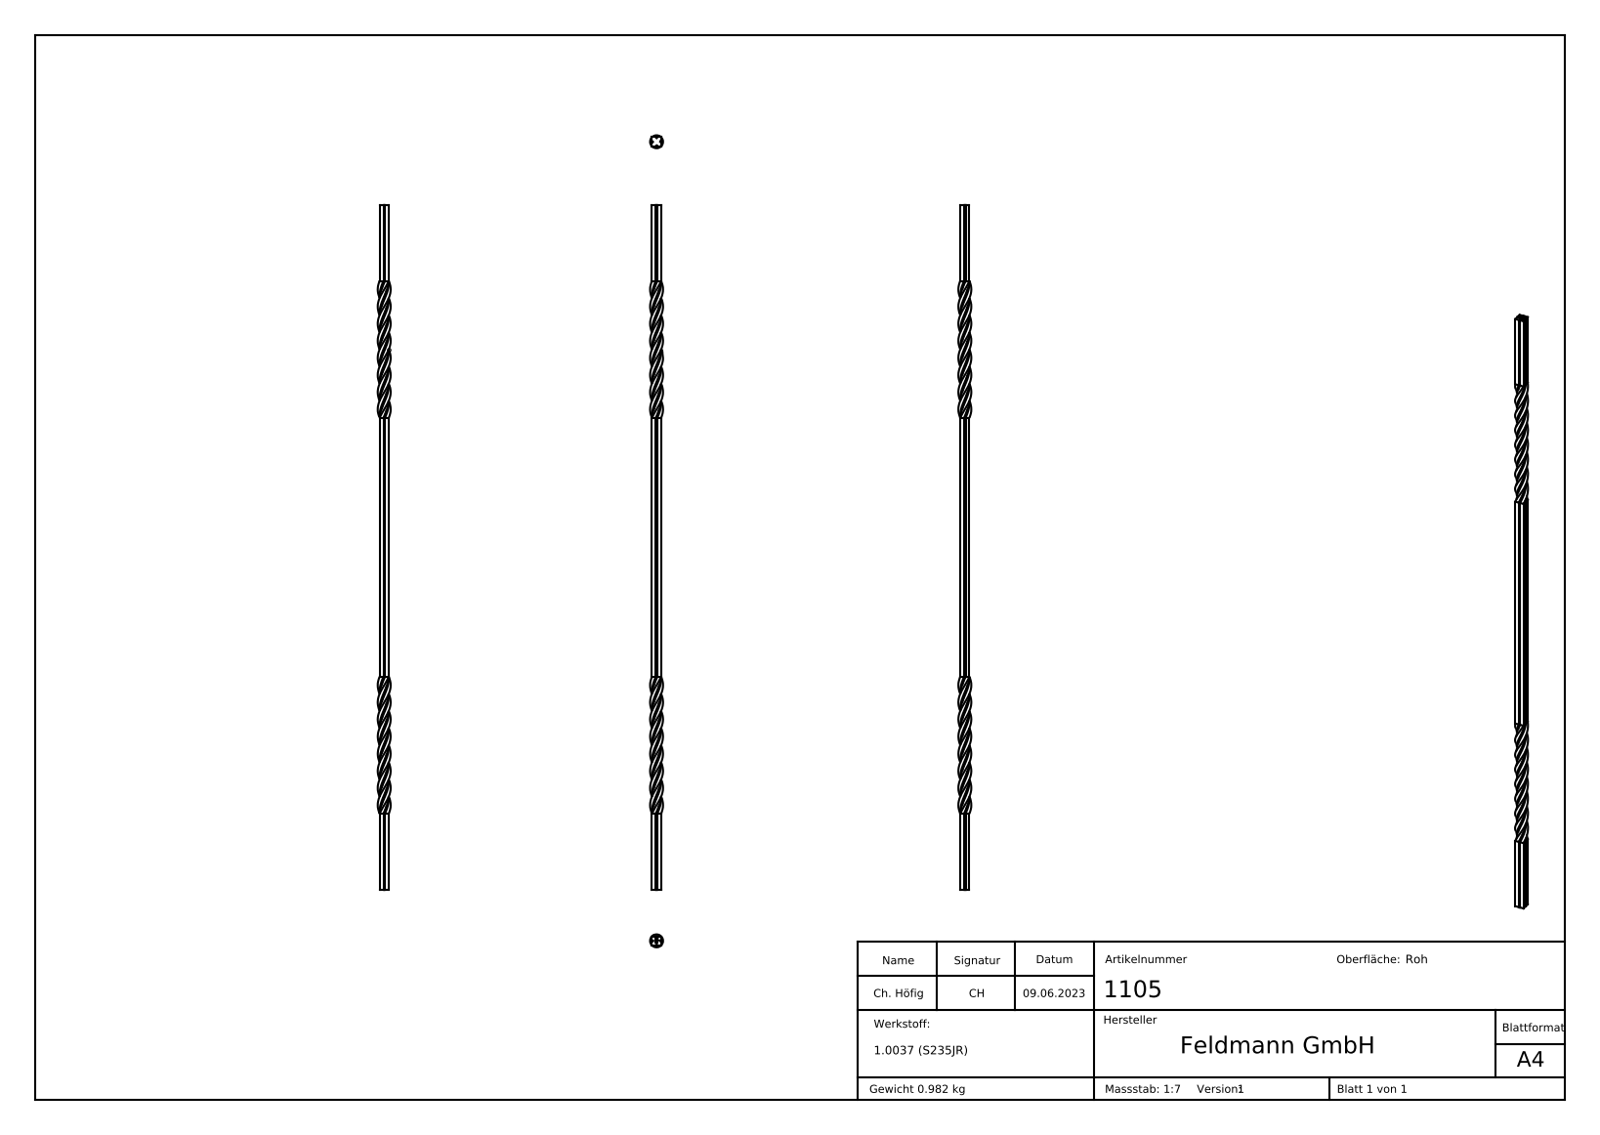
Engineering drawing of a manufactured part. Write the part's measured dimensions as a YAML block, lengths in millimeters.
part_name: "1105"
step_written_by: "SolidWorks 2018 (CONFIG_CONTROL_DESIGN)"
units: millimeters
bodies: {solids: 1, faces: 278, planar: 161, cylindrical: 0, other: 117}
overall_size: [900, 16.97, 16.97]
volume: 125856
surface_area: 47107
face_to_face_distances: [12, 7.07, 7.08, 7.06, 900, 899.9, 1.76, 2.32, 1.78, 1.02]
